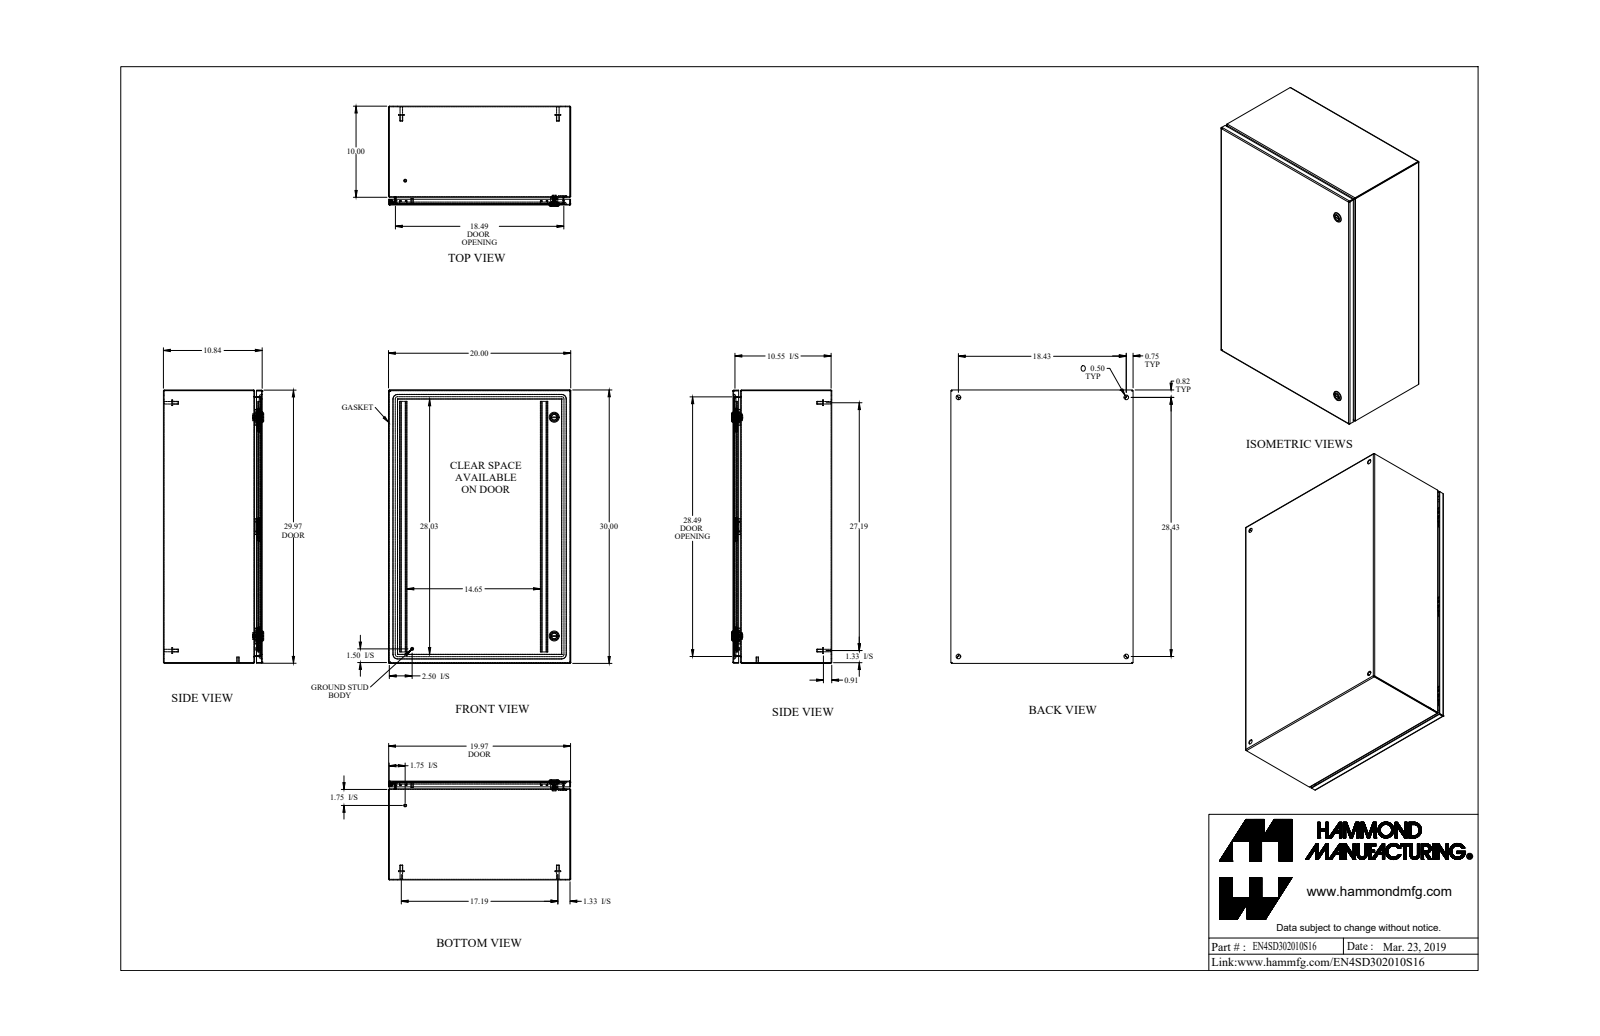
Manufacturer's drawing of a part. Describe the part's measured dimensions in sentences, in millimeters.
The part is named "EN4SD302010S16". Its 3-D file was written by "SolidWorks 2019 (AUTOMOTIVE_DESIGN)". It is 33 solids with 891 faces: 423 planar, 300 cylindrical and 168 other. Overall it measures 762 by 508 by 279.5 millimeters. Its volume is 3 050 000 cubic millimeters and its surface area 3 379 000 square millimeters. Round holes: 6 of diameter 12.7, 2 of diameter 5, 2 of diameter 9.8, 2 of diameter 16, 2 of diameter 19.5, 1 of diameter 4.4, 1 of diameter 6.1, 1 of diameter 6.1. Round bosses or shafts: 6 of diameter 8, 4 of diameter 15.9, 4 of diameter 7, 2 of diameter 27.9, 2 of diameter 19.9, 2 of diameter 15.9, 2 of diameter 13.3, 2 of diameter 6.4. Partial cylindrical surfaces (rounded edges, fillets, slot ends): 16 of radius 0.9, 16 of radius 2.7, 16 of radius 6.4, 12 of radius 0.3, 12 of radius 1.2, 8 of radius 2.5, 6 of radius 0.2, 6 of radius 1.6. The main face-to-face distances are 1.8, 273.6, 271.7, 275.4, 506.2, 760.2, 504.3, 508, 758.3, 762. The hole center spacings are 468.1, 722.1, 860.5, 60.8, 62.4, 446.4, 446.6, 609.6.
